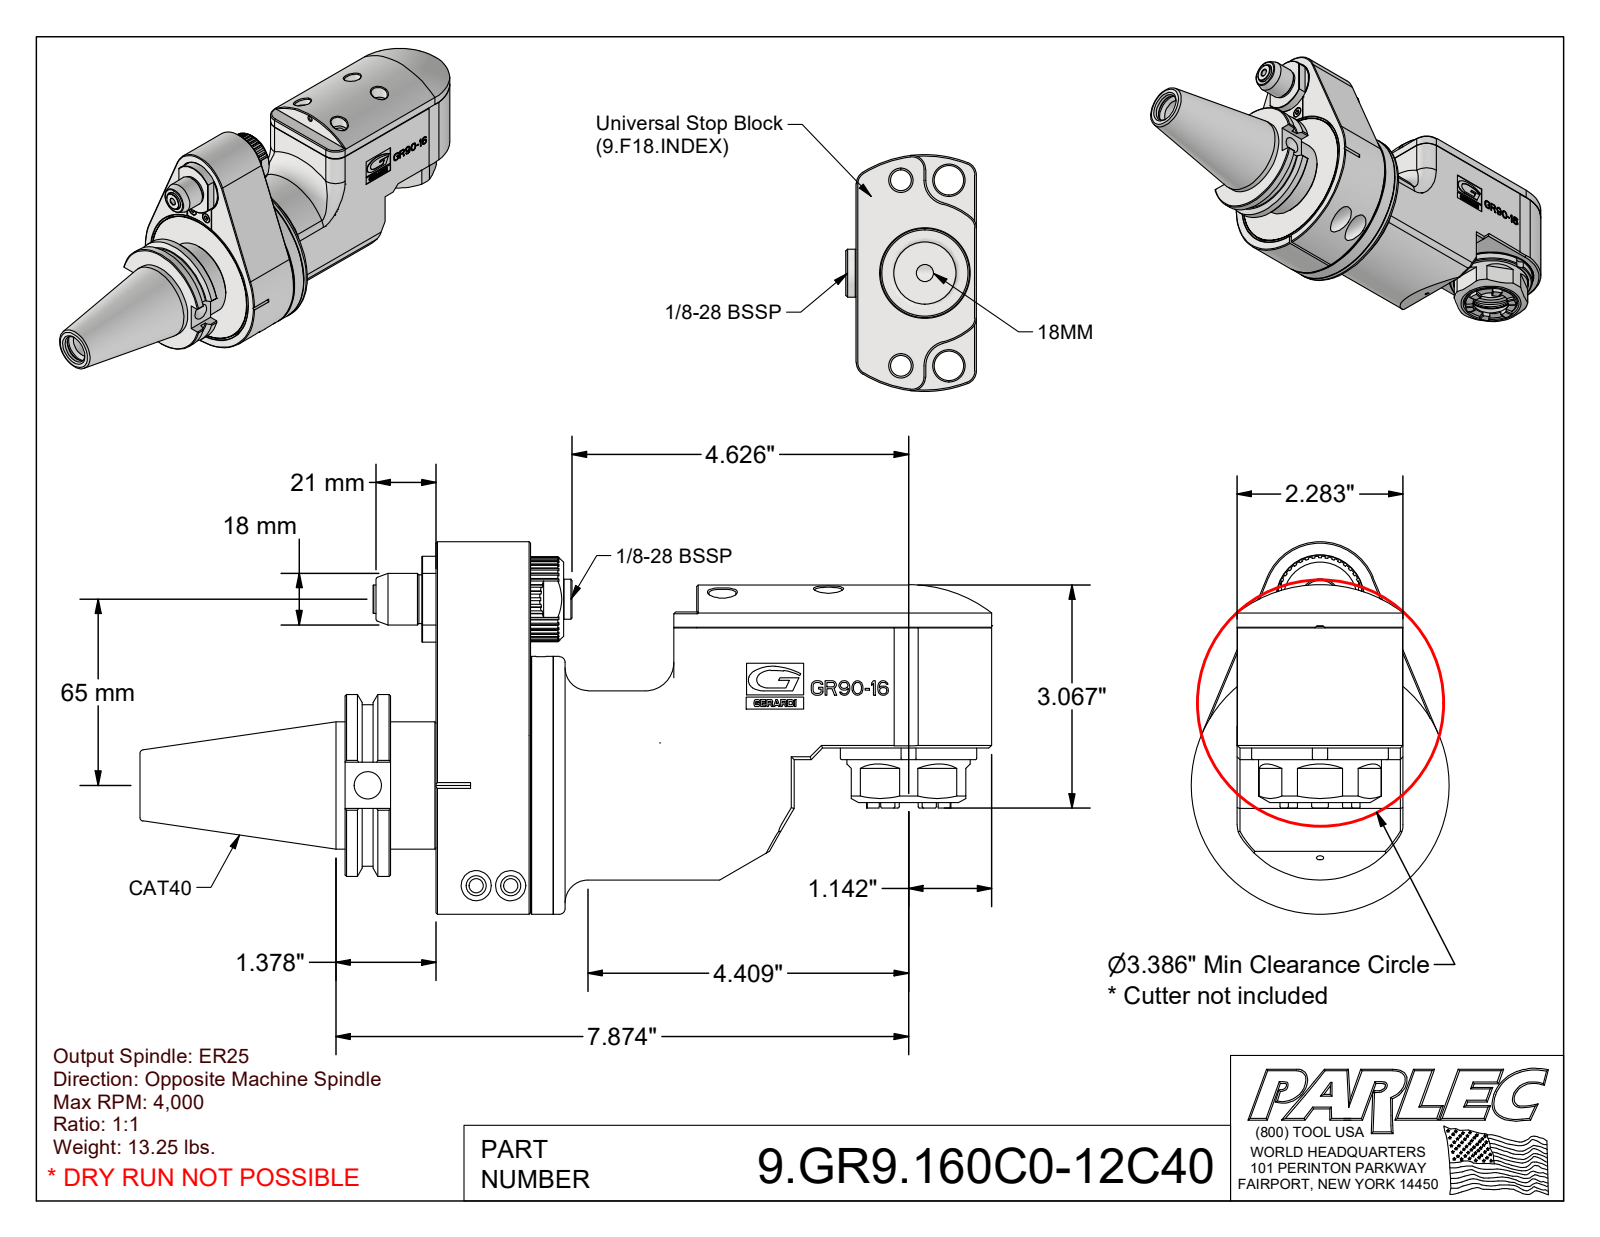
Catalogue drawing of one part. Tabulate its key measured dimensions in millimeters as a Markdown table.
| quantity | value |
| --- | --- |
| part name | 9.GR9.160C0-12C40; 9_GR9_16000RI; 9_GA1_446_1 (Classic, Type 1, Cat40, 65mm) |
| STEP written by | Autodesk Inventor 2022 (AUTOMOTIVE_DESIGN) |
| units | millimeters |
| bodies | 5 solids, 1543 faces (926 planar, 316 cylindrical, 301 other) |
| overall size | 297.4 × 130 × 90 |
| volume | 850 300 mm³ |
| surface area | 188 600 mm² |
| round holes (diameter × count) | 4.2 × 12, 2.5 × 5, 5 × 5, 5.5 × 5, 2.2 × 4, 3 × 4, 9.5 × 4, 3.2 × 3, 14 × 3, 18 × 3, 2 × 2, 4 × 2 |
| round bosses / shafts (diameter × count) | 30 × 3, 6 × 2, 4 × 2, 90 × 1, 78 × 1, 63.5 × 1, 56.4 × 1, 48 × 1 |
| partial cylindrical surfaces (radius × count) | 8 × 8, 35 × 8, 3 × 6, 1 × 4, 5 × 4, 2.2 × 2, 26.5 × 2, 26.7 × 2 |
| main face-to-face distances | 33, 5, 8, 25, 58, 0.5, 3, 25.5, 17, 30 |
| hole center spacings | 37.5, 27.5, 21.2, 23, 8, 15, 19.4, 26 |
